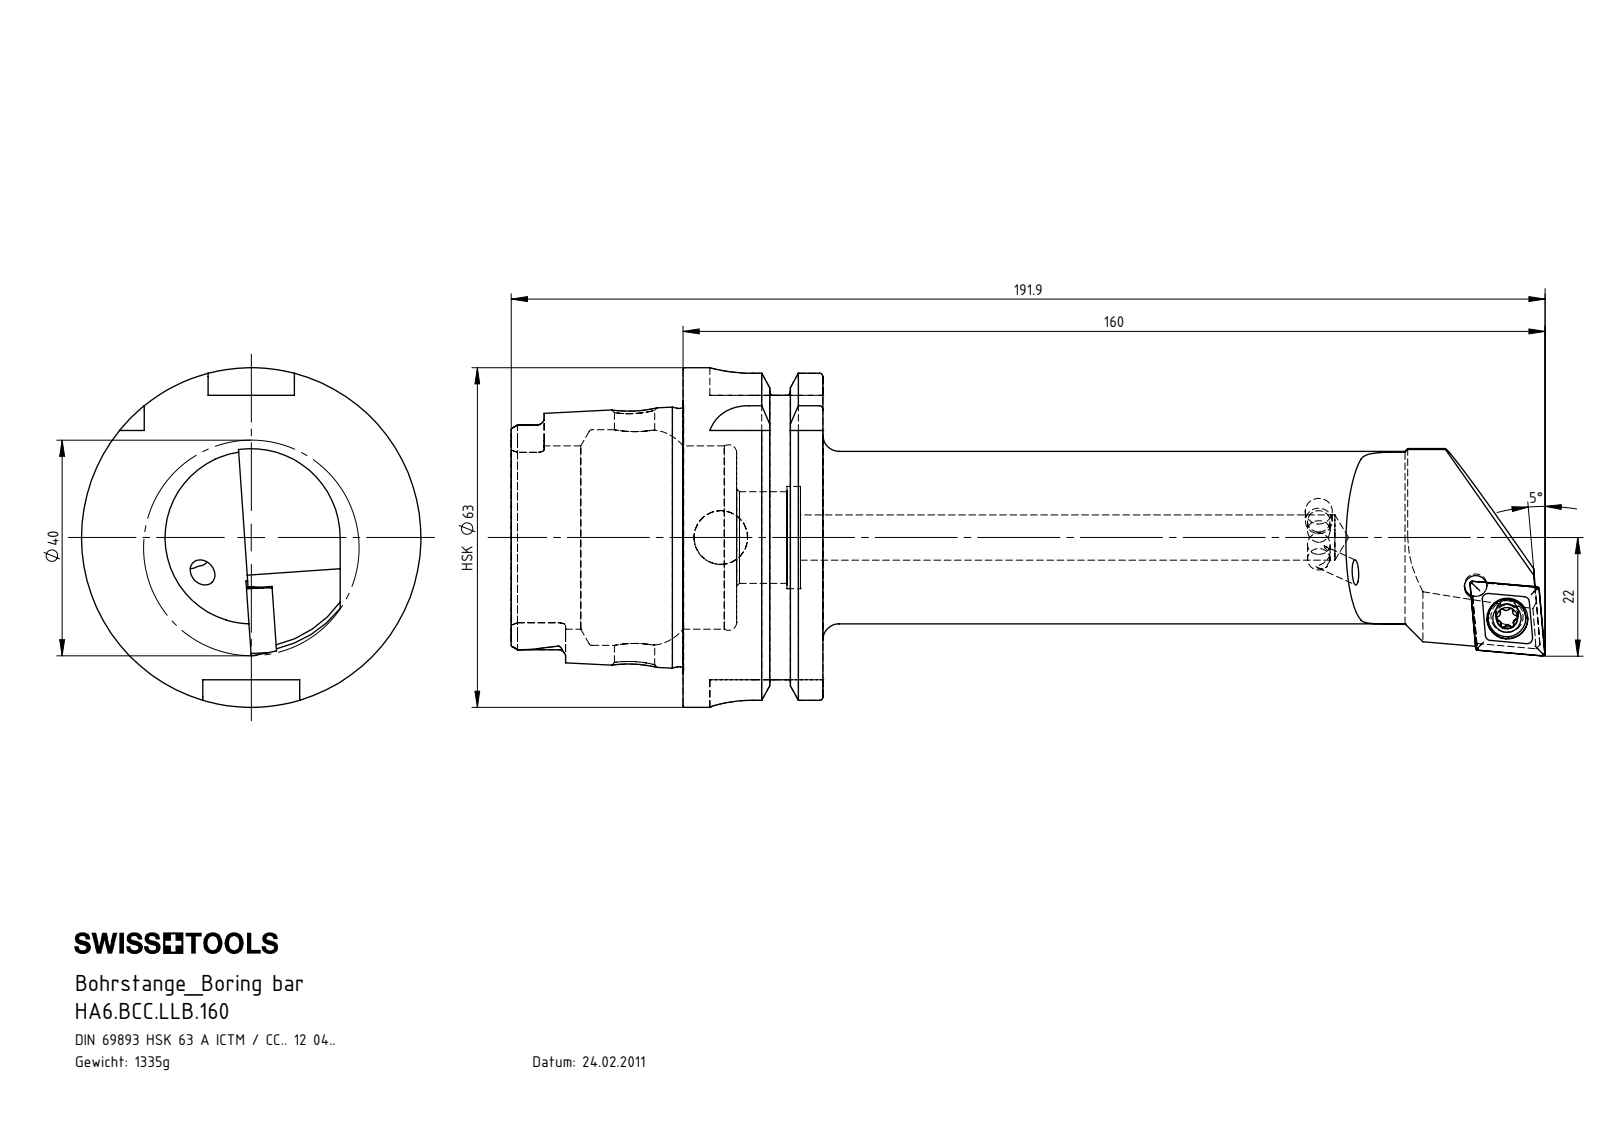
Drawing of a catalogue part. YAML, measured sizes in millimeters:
part_name: "CCMT120404; HA6.BCC.LLB.160; WCC-ER2.001.010_A; HA6-BCC.LLB.160_A (+1 more)"
step_written_by: "SolidWorks 2017 (AUTOMOTIVE_DESIGN)"
units: millimeters
bodies: {solids: 5, faces: 298, planar: 71, cylindrical: 91, other: 136}
overall_size: [191.86, 63, 63]
volume: 170193
surface_area: 38768
round_holes:
  - {diameter: 4.2, count: 4}
  - {diameter: 4, count: 1}
  - {diameter: 5.5, count: 1}
  - {diameter: 7.5, count: 1}
  - {diameter: 7.6, count: 1}
  - {diameter: 8.4, count: 1}
  - {diameter: 10, count: 1}
  - {diameter: 17, count: 1}
  - {diameter: 19, count: 1}
  - {diameter: 34, count: 1}
  - {diameter: 40, count: 1}
round_bosses_or_shafts:
  - {diameter: 5, count: 2}
  - {diameter: 63, count: 1}
  - {diameter: 54.95, count: 1}
  - {diameter: 47.94, count: 1}
  - {diameter: 32, count: 1}
  - {diameter: 7, count: 1}
partial_cylinders:
  - {radius: 0.39, count: 6}
  - {radius: 1.4, count: 6}
  - {radius: 8, count: 4}
  - {radius: 0.69, count: 3}
  - {radius: 0.69, count: 3}
  - {radius: 2.82, count: 2}
  - {radius: 2.88, count: 2}
  - {radius: 3, count: 1}
face_to_face_distances: [25.95, 16, 9.95, 31.9, 41.85, 57.85, 52.8, 21.8, 11.85, 53.7]
hole_center_spacings: [8.06, 8.32]
